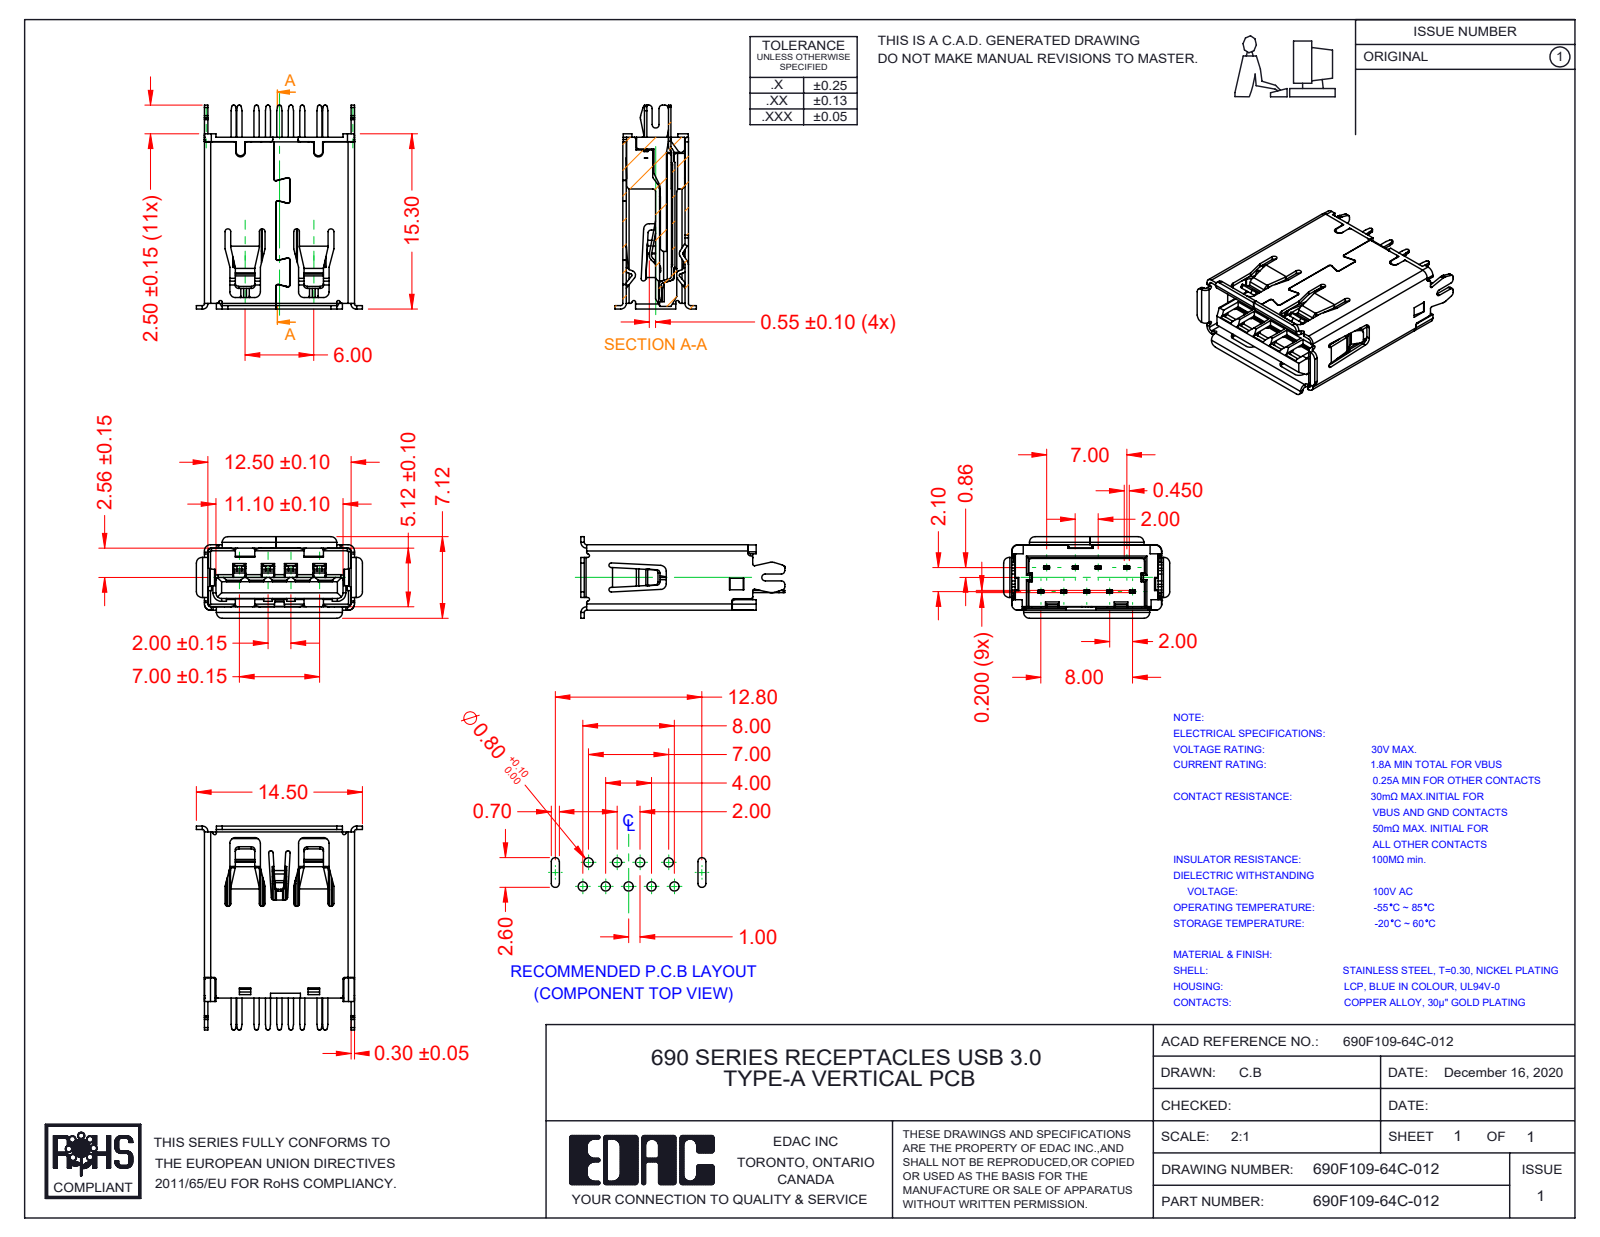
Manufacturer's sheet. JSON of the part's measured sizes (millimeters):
{"part_name": "Contact 2.0 690F109-64C-012; Contact 3.0 690F109-64C-012; Insulator2 690F109-64C-012; Shell 690F109-64C-012 (+2 more)", "step_written_by": "SolidWorks 2020 (AUTOMOTIVE_DESIGN)", "units": "millimeters", "bodies": {"solids": 12, "faces": 2136, "planar": 1377, "cylindrical": 635, "other": 124}, "overall_size": [17.8, 14.5, 7.12], "volume_mm3": 522, "surface_area_mm2": 2611, "partial_cylinders_radius": [[0.15, 105], [0.1, 46], [0.2, 41], [0.3, 31], [0.13, 30], [0.5, 24], [0.25, 20], [1, 13]], "face_to_face_distances": [5.42, 5.72, 5.12, 12.8, 3.5, 2.56, 2.86, 1.84, 1.92, 1.02]}
